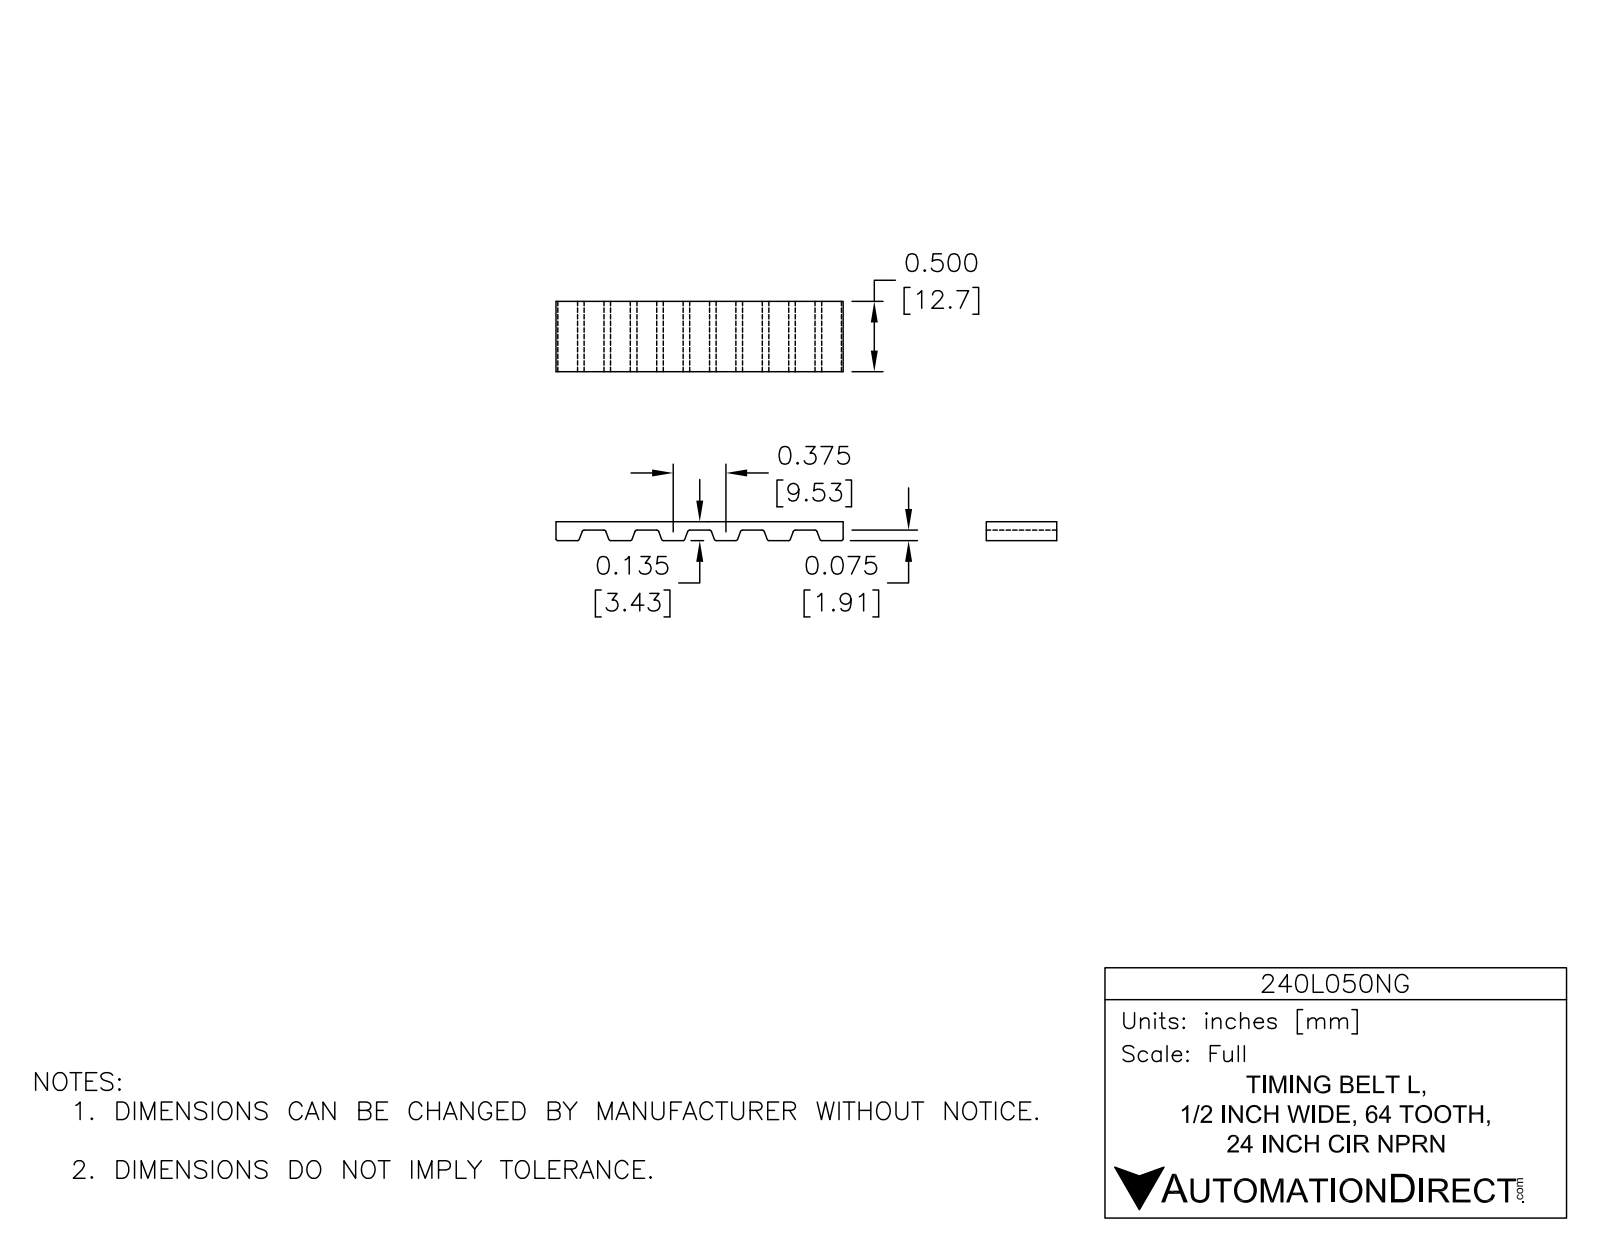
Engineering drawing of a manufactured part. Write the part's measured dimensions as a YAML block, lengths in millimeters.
part_name: "240L050NG"
step_written_by: "SolidWorks 2014 (AUTOMOTIVE_DESIGN)"
units: millimeters
bodies: {solids: 1, faces: 527, planar: 233, cylindrical: 294, other: 0}
overall_size: [261.3, 76.2, 12.7]
volume: 17730
surface_area: 19980
partial_cylinders:
  - {radius: 0.5, count: 252}
  - {radius: 36.4, count: 2}
  - {radius: 38.1, count: 2}
face_to_face_distances: [1.7, 74.5, 76.2, 12.7, 72.9, 3.6, 72.6, 1.9, 71, 69.1]
